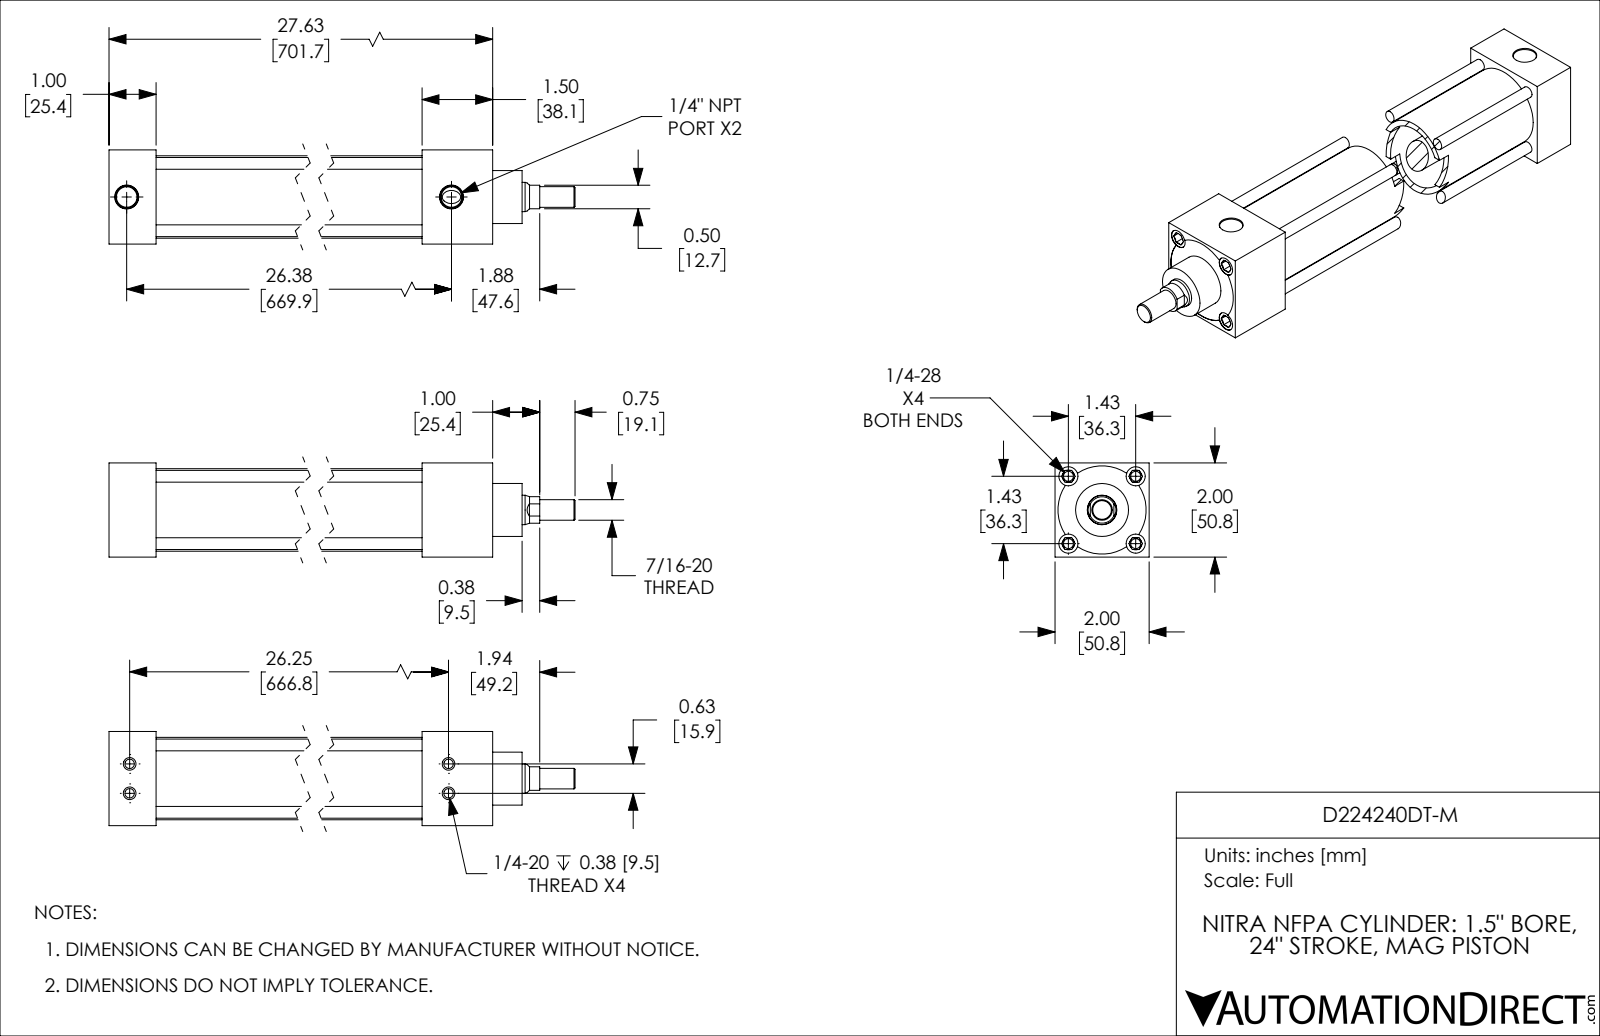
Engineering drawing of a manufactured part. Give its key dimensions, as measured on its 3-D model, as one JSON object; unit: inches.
{"part_name": "D224240DT-M_BODY; D224240DT-M_PISTON_KK1; D224240DT-M", "step_written_by": "SolidWorks 2019 (CONFIG_CONTROL_DESIGN)", "units": "inches", "bodies": {"solids": 2, "faces": 203, "planar": 58, "cylindrical": 65, "other": 80}, "overall_size": [29.375, 2, 2], "volume_in3": 40.56, "surface_area_in2": 444.9, "round_holes": [[0.201, 4], [0.213, 4], [0.406, 4], [0.438, 2], [0.626, 1], [1.501, 1]], "round_bosses_or_shafts": [[0.25, 4], [1.751, 1], [1.499, 1], [1.125, 1], [0.624, 1], [0.437, 1]], "partial_cylinders_radius": [[0.281, 1], [0.937, 1]], "face_to_face_distances": [2, 1, 26.125, 25.125, 27.62, 26.62, 1.495, 1.125, 2.125, 24], "hole_center_spacings": [0.319, 1.011, 1.43, 0.625, 2.022, 26.25, 26.257, 26.314]}
